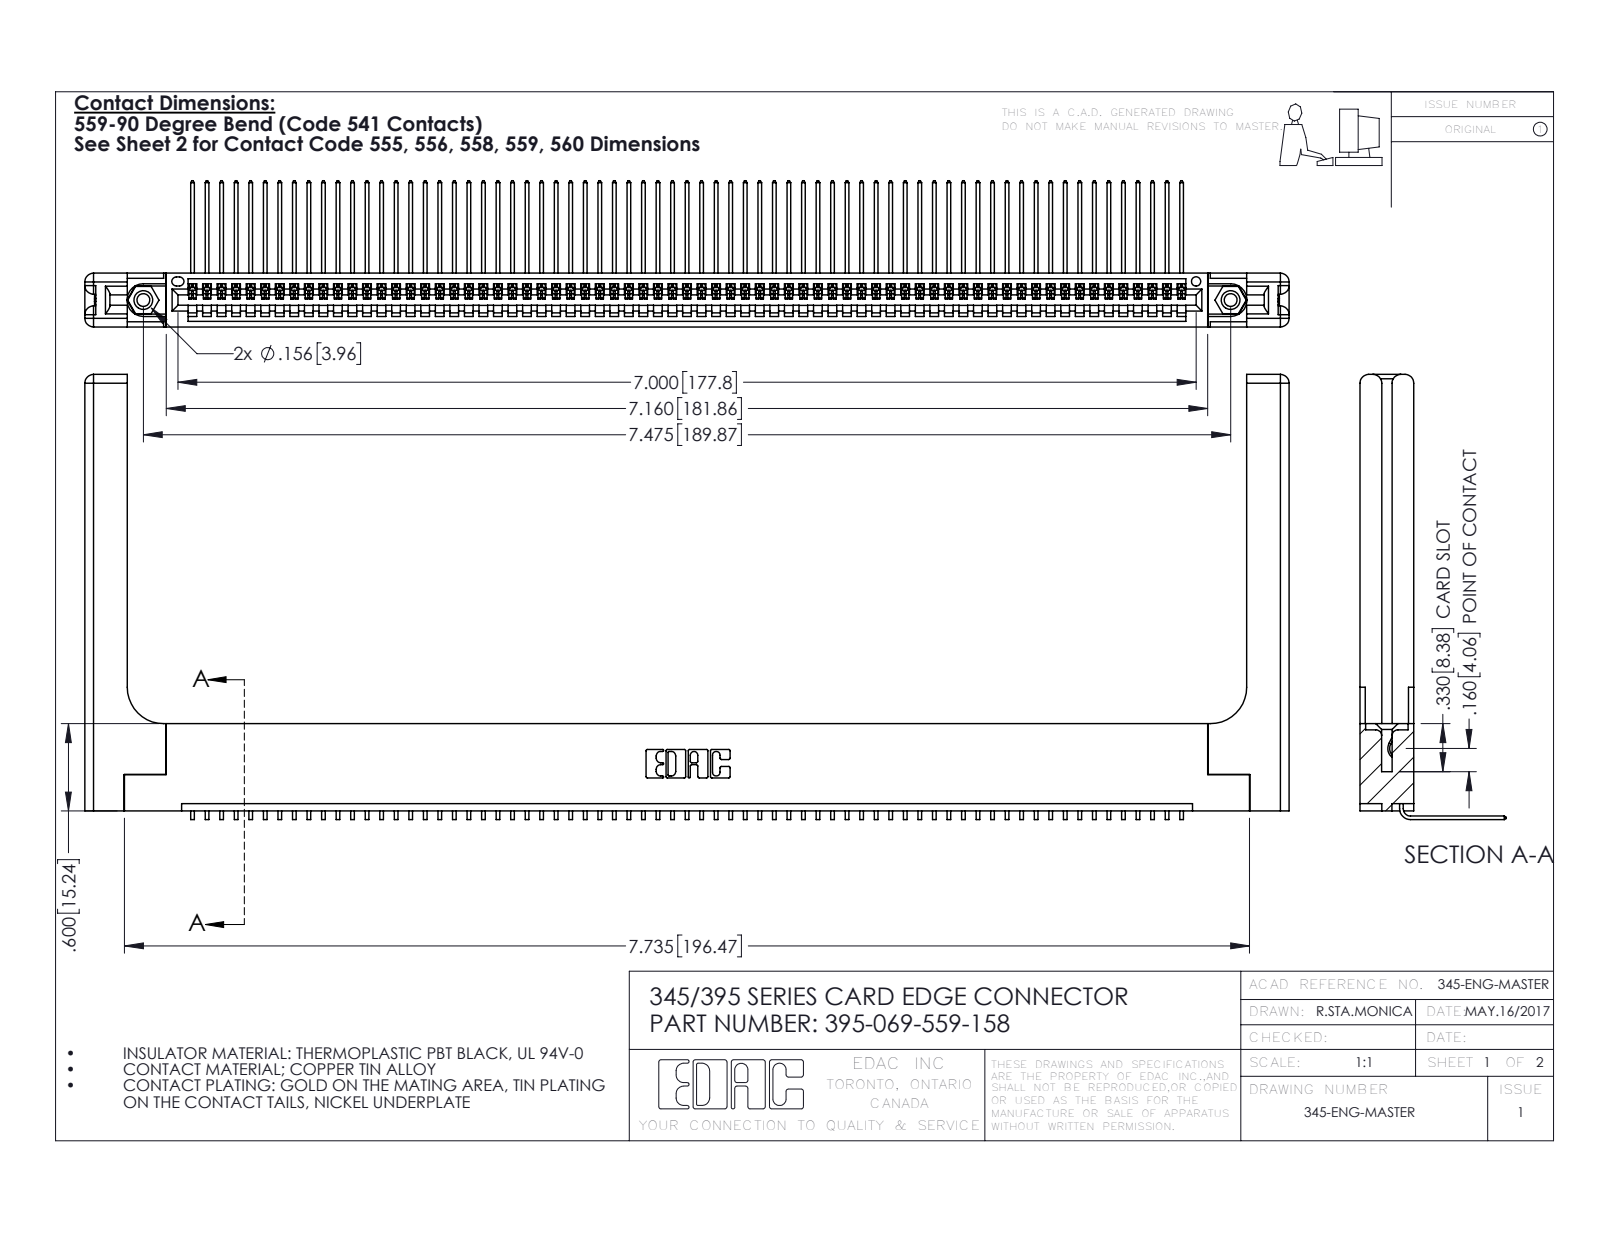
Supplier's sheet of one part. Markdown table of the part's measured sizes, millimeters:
| quantity | value |
| --- | --- |
| part name | 345-220-058_345-220-058; 395-069-559-158; 345-292-001_558 559 Tail - 1; 345 Part_Flush Mounting Lugs - 0.156 Dia-TH (+1 more) |
| STEP written by | SolidWorks 2016 (CONFIG_CONTROL_DESIGN) |
| units | millimeters |
| bodies | 74 solids, 4522 faces (3126 planar, 1336 cylindrical, 60 other) |
| overall size | 210.3 × 77.7 × 25.5 |
| volume | 28 920 mm³ |
| surface area | 34 170 mm² |
| round holes (diameter × count) | 2.3 × 2, 3.2 × 2, 4 × 2, 1.6 × 1 |
| round bosses / shafts (diameter × count) | 3.9 × 2 |
| partial cylindrical surfaces (radius × count) | 0.2 × 138, 0.3 × 22, 1.5 × 16, 0.2 × 6, 0.8 × 6, 0.7 × 3, 0.8 × 2, 0.8 × 2 |
| main face-to-face distances | 1.8, 9.4, 7.6, 5.1, 2.5, 6.9, 0.6, 5.7, 3.8, 3.8 |
| hole center spacings | 6.9, 183.9, 189.9 |
